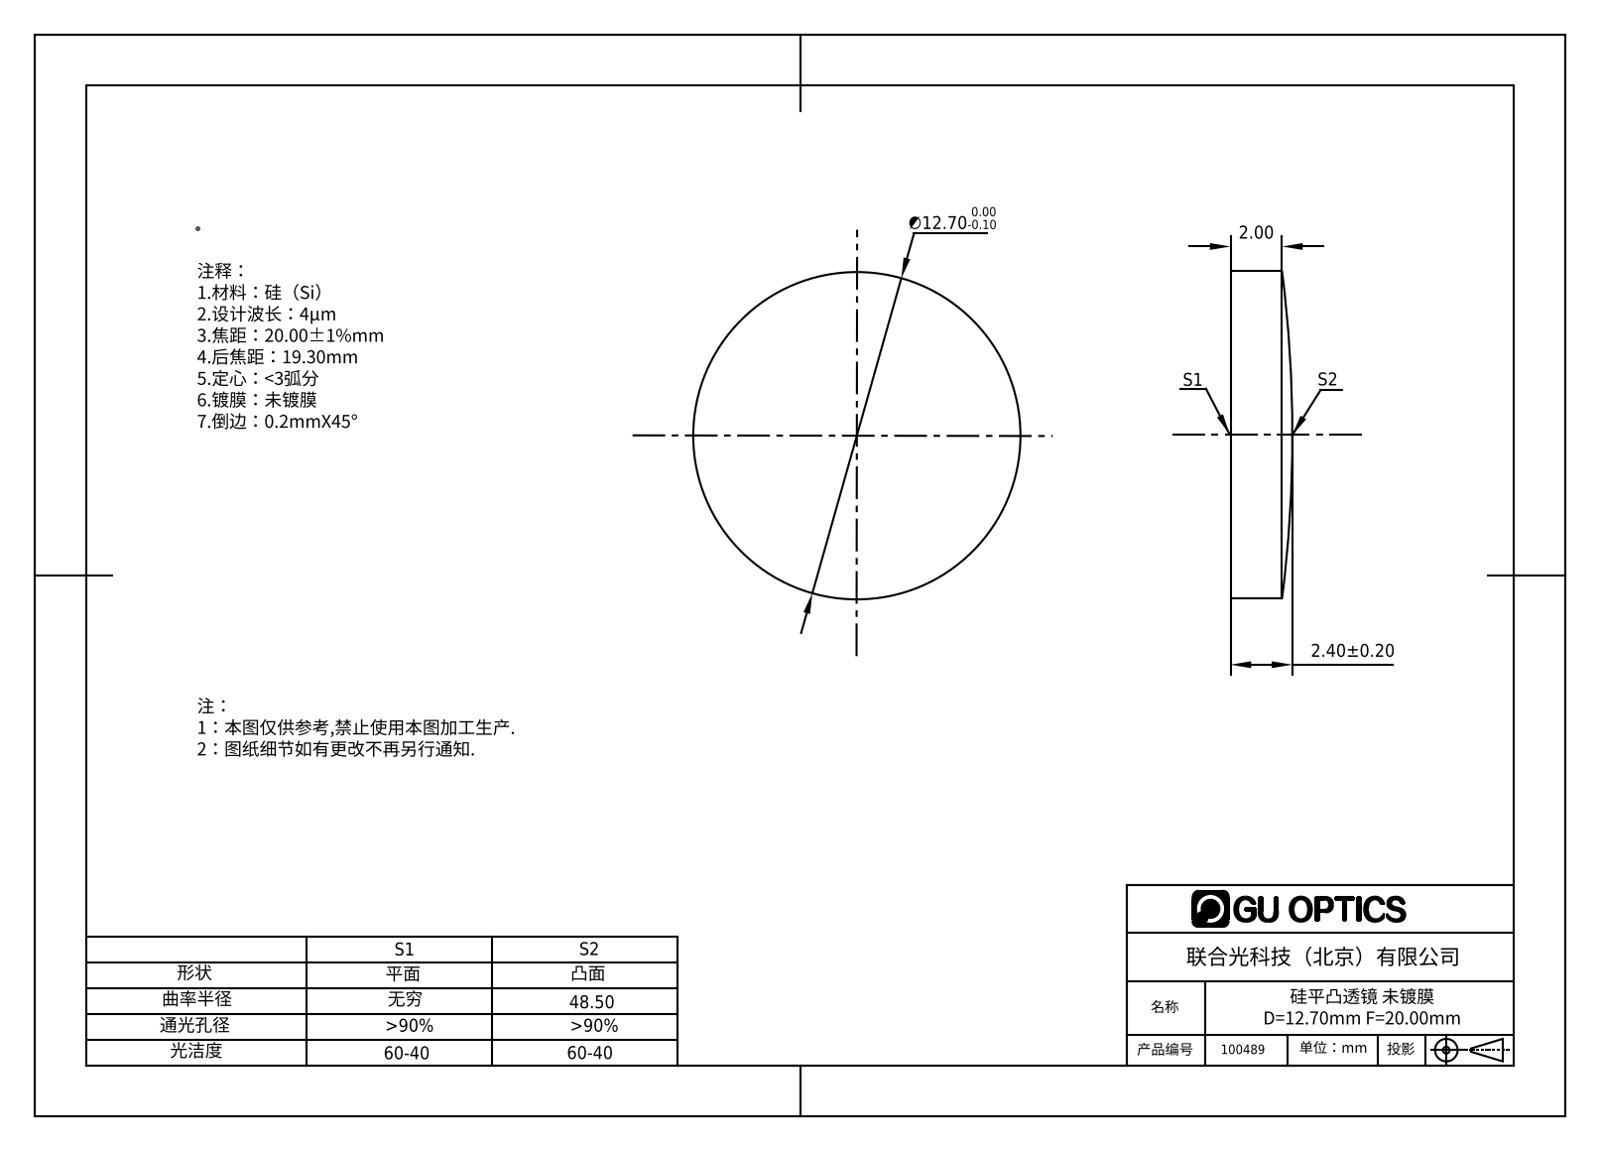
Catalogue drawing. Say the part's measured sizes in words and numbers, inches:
The part is named "100489". Its 3-D file was written by "SolidWorks 2016 (AUTOMOTIVE_DESIGN)". It is 1 solid with 5 faces: 1 planar, 2 cylindrical and 2 other. Overall it measures 0.5 by 0.5 by 0.094 inches. Its volume is 0.017 cubic inches and its surface area 0.518 square inches. Round bosses or shafts: 1 of diameter 0.5.
